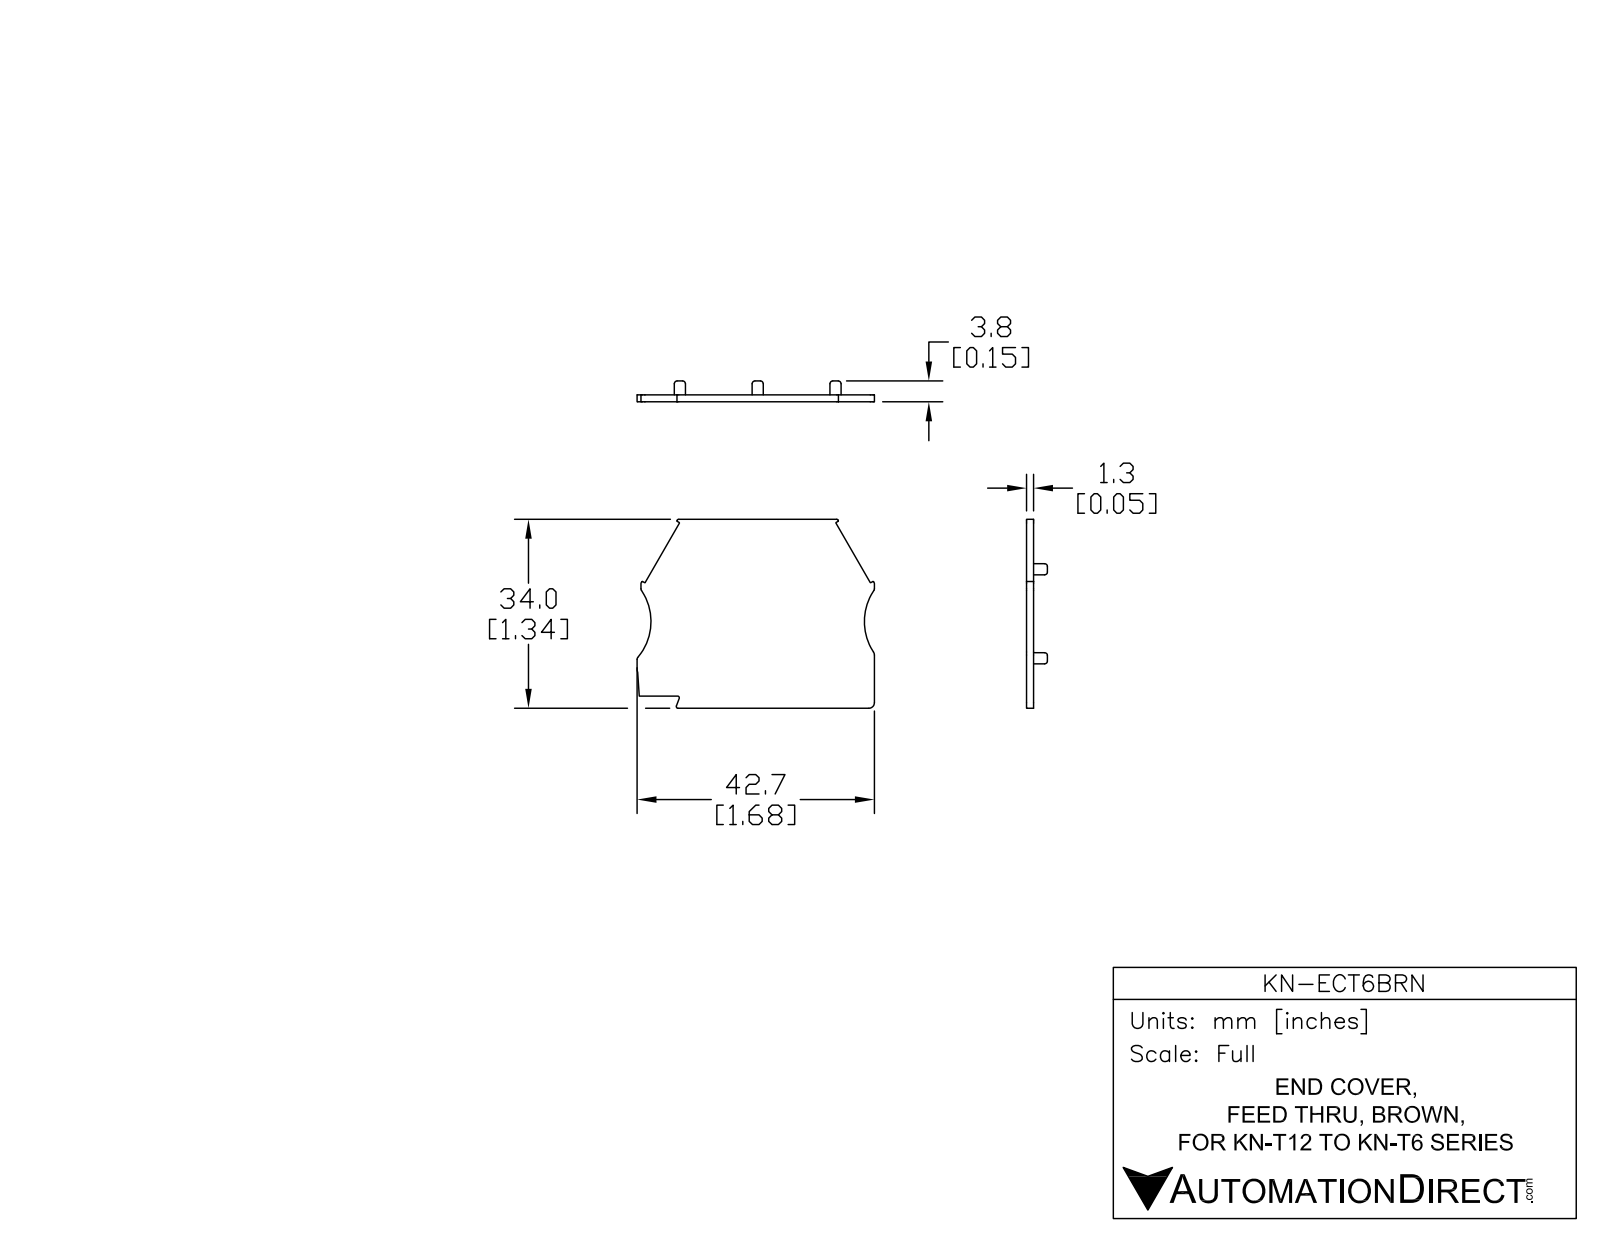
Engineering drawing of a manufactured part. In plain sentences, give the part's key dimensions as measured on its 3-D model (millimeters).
The part is named "KN-ECT6GRY". Its 3-D file was written by "SolidWorks 2014 (AUTOMOTIVE_DESIGN)". It is 1 solid with 72 faces: 27 planar, 39 cylindrical and 6 other. Overall it measures 42.7 by 34 by 3.75 millimeters. Its volume is 1 642 cubic millimeters and its surface area 2 839 square millimeters. Round holes: 3 of diameter 0.75. Round bosses or shafts: 3 of diameter 2. Partial cylindrical surfaces (rounded edges, fillets, slot ends): 8 of radius 0.1, 7 of radius 0.3, 4 of radius 0.5, 2 of radius 1, 2 of radius 10. The main face-to-face distances are 1.24, 34.01, 2.2, 31.81, 42.7, 0.7, 42, 2.5, 3.74, 12.5. The hole center spacings are 21.24, 21.25, 28.
